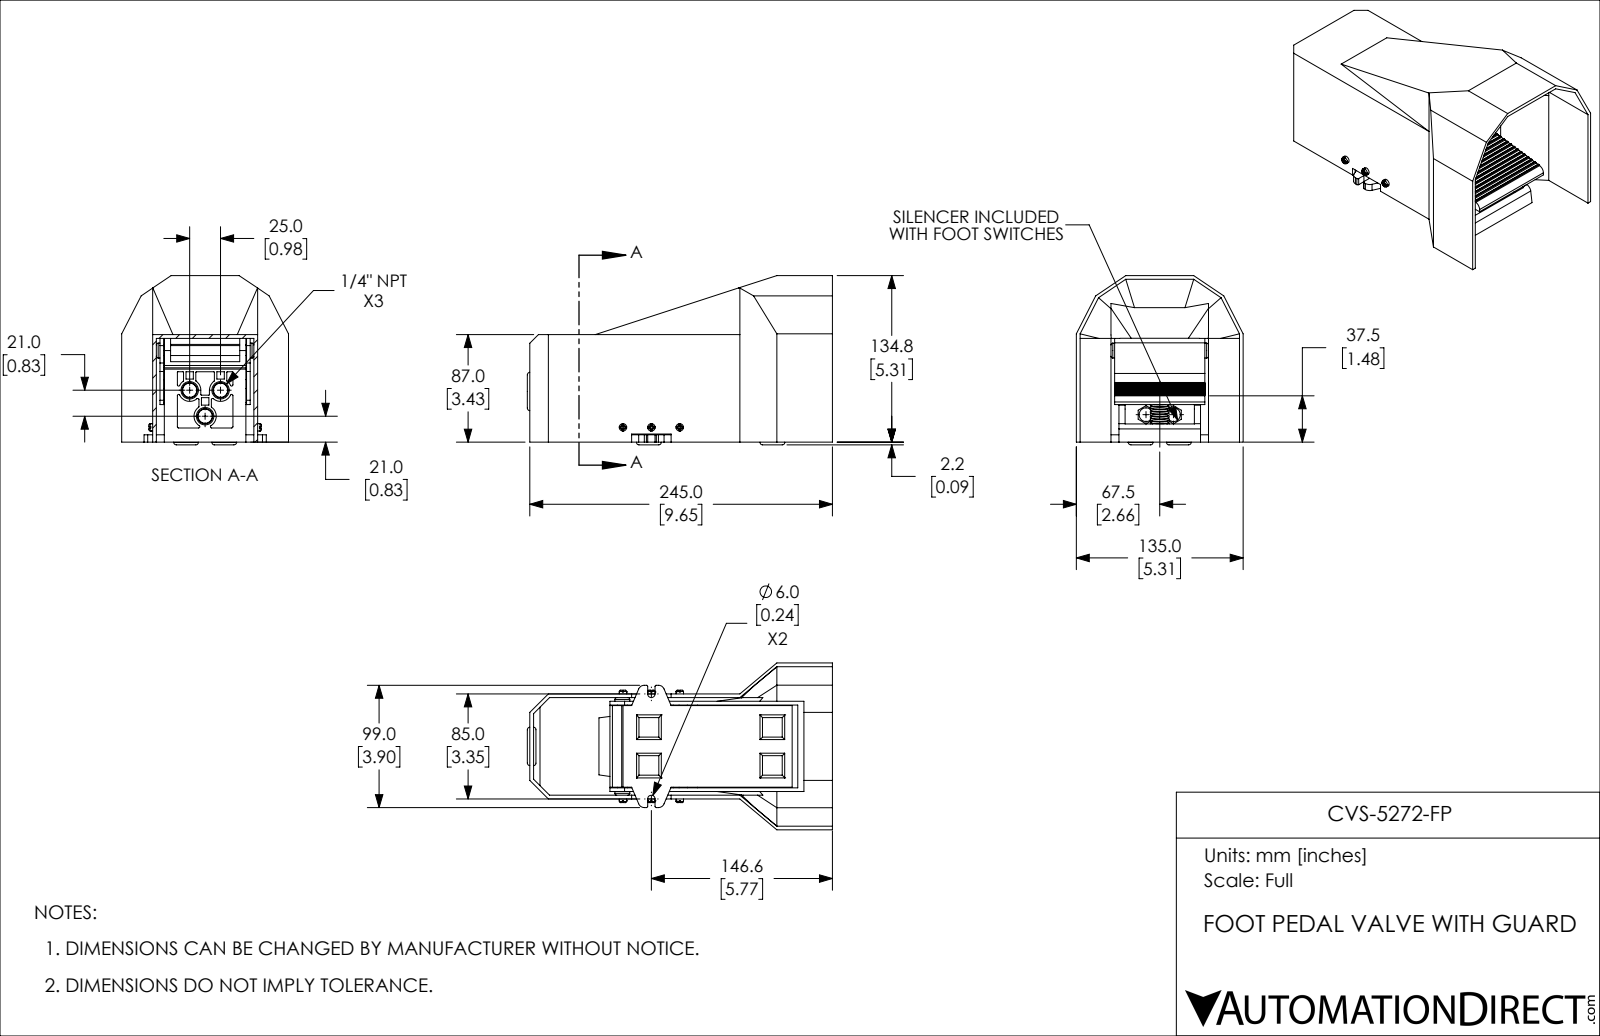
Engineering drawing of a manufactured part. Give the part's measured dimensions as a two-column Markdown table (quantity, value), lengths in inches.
| quantity | value |
| --- | --- |
| part name | CVS-5272-FP |
| STEP written by | SolidWorks 2021 (CONFIG_CONTROL_DESIGN) |
| units | inches |
| bodies | 5 solids, 641 faces (358 planar, 173 cylindrical, 110 other) |
| overall size | 9.724 × 5.394 × 5.315 |
| volume | 39.07 in³ |
| surface area | 405.8 in² |
| round holes (diameter × count) | 0.63 × 2, 0.394 × 1, 0.472 × 1, 0.787 × 1 |
| round bosses / shafts (diameter × count) | 0.512 × 4, 0.236 × 3, 0.787 × 2, 0.437 × 2, 0.472 × 1, 0.315 × 1 |
| partial cylindrical surfaces (radius × count) | 0.02 × 32, 0.039 × 15, 0.197 × 11, 0.079 × 7, 0.394 × 4, 0.118 × 3, 0.354 × 3, 0.087 × 2 |
| main face-to-face distances | 0.118, 3.228, 3.11, 0.197, 0.984, 4.213, 1.102, 4.094, 0.236, 3.976 |
